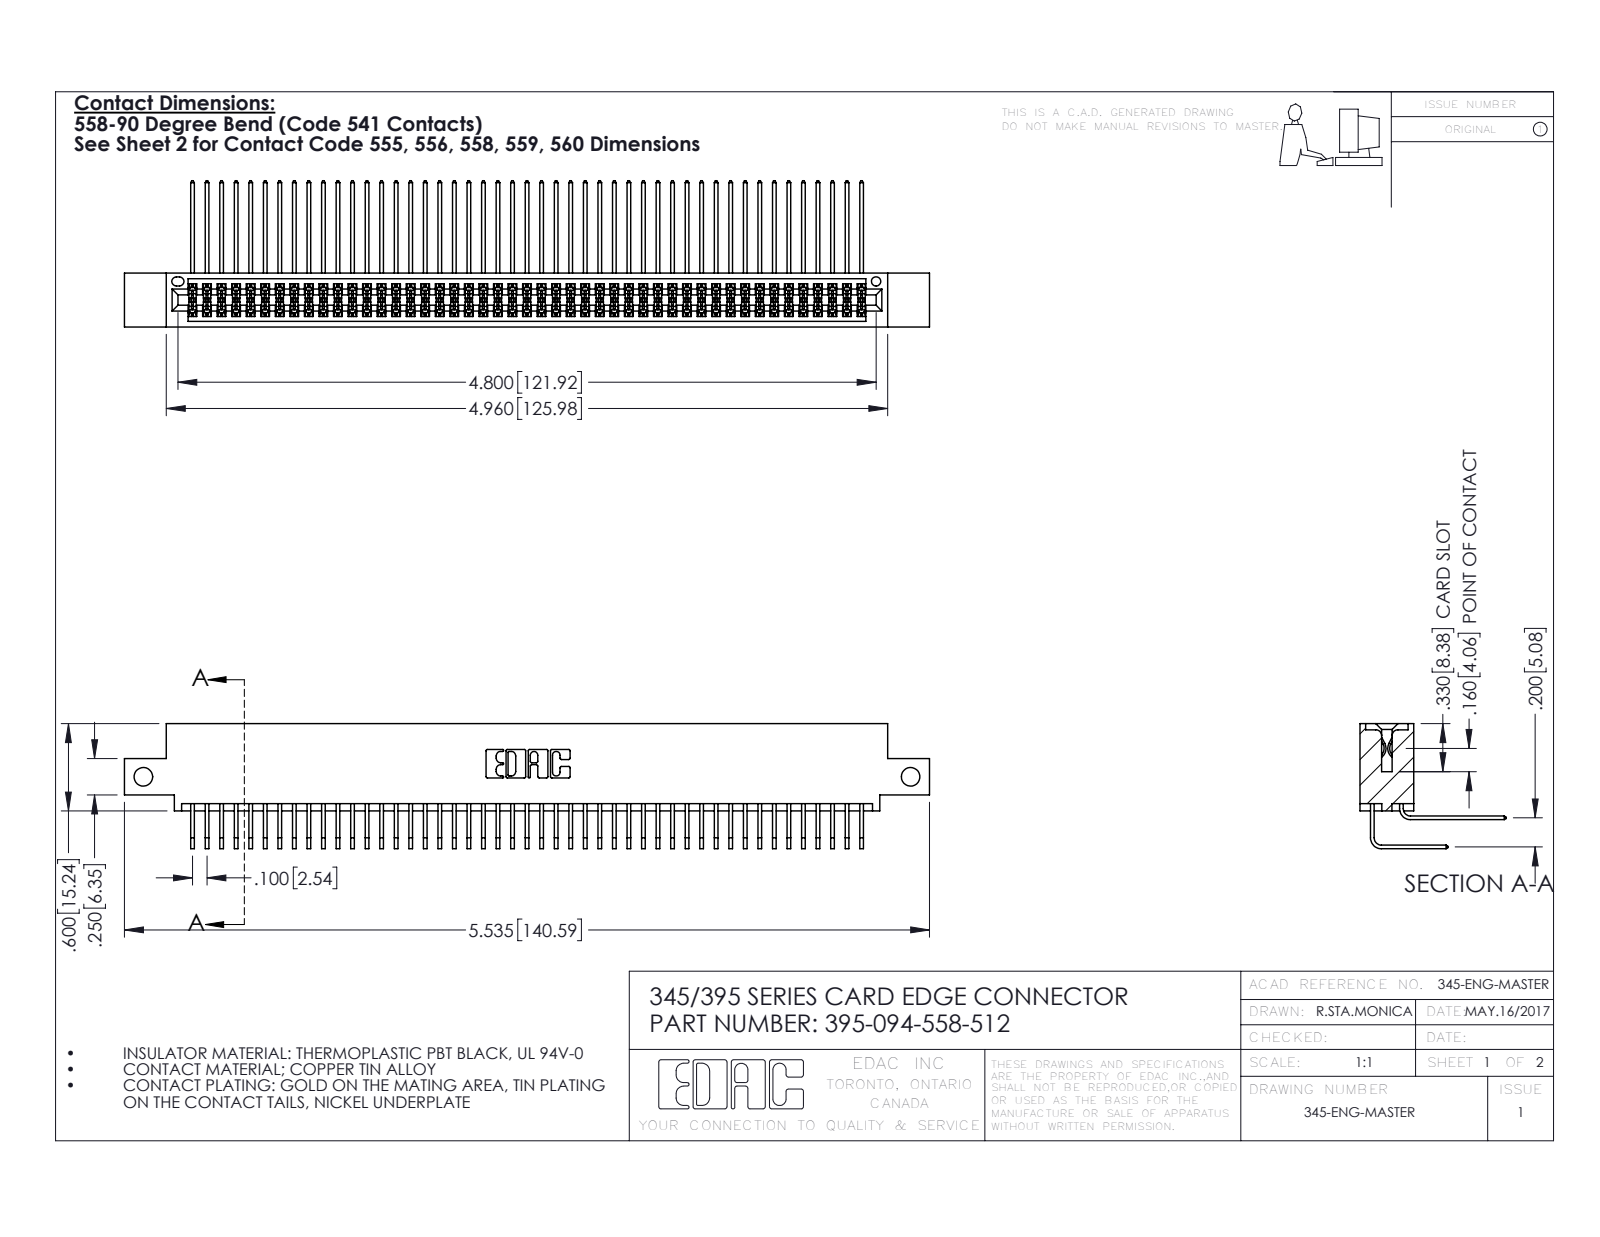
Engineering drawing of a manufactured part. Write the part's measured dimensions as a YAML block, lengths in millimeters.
part_name: "345-292-001_558 559 Tail - 1; 345 Part_0.110 Offset - Side Mount; 345-292-001_558 Tail - 2; 395-094-558-512"
step_written_by: "SolidWorks 2016 (CONFIG_CONTROL_DESIGN)"
units: millimeters
bodies: {solids: 95, faces: 5018, planar: 3374, cylindrical: 1644, other: 0}
overall_size: [140.6, 25.5, 21.8]
volume: 14100
surface_area: 23430
round_holes:
  - {diameter: 3.3, count: 2}
  - {diameter: 1.6, count: 1}
partial_cylinders:
  - {radius: 0.2, count: 142}
  - {radius: 0.3, count: 22}
  - {radius: 0.2, count: 6}
  - {radius: 0.8, count: 6}
  - {radius: 0.7, count: 3}
  - {radius: 0.4, count: 2}
  - {radius: 0.5, count: 2}
  - {radius: 0.6, count: 2}
face_to_face_distances: [1.8, 7.6, 5.1, 9.4, 2.5, 6.9, 0.6, 5.7, 0.6, 4.4]
hole_center_spacings: [134]
